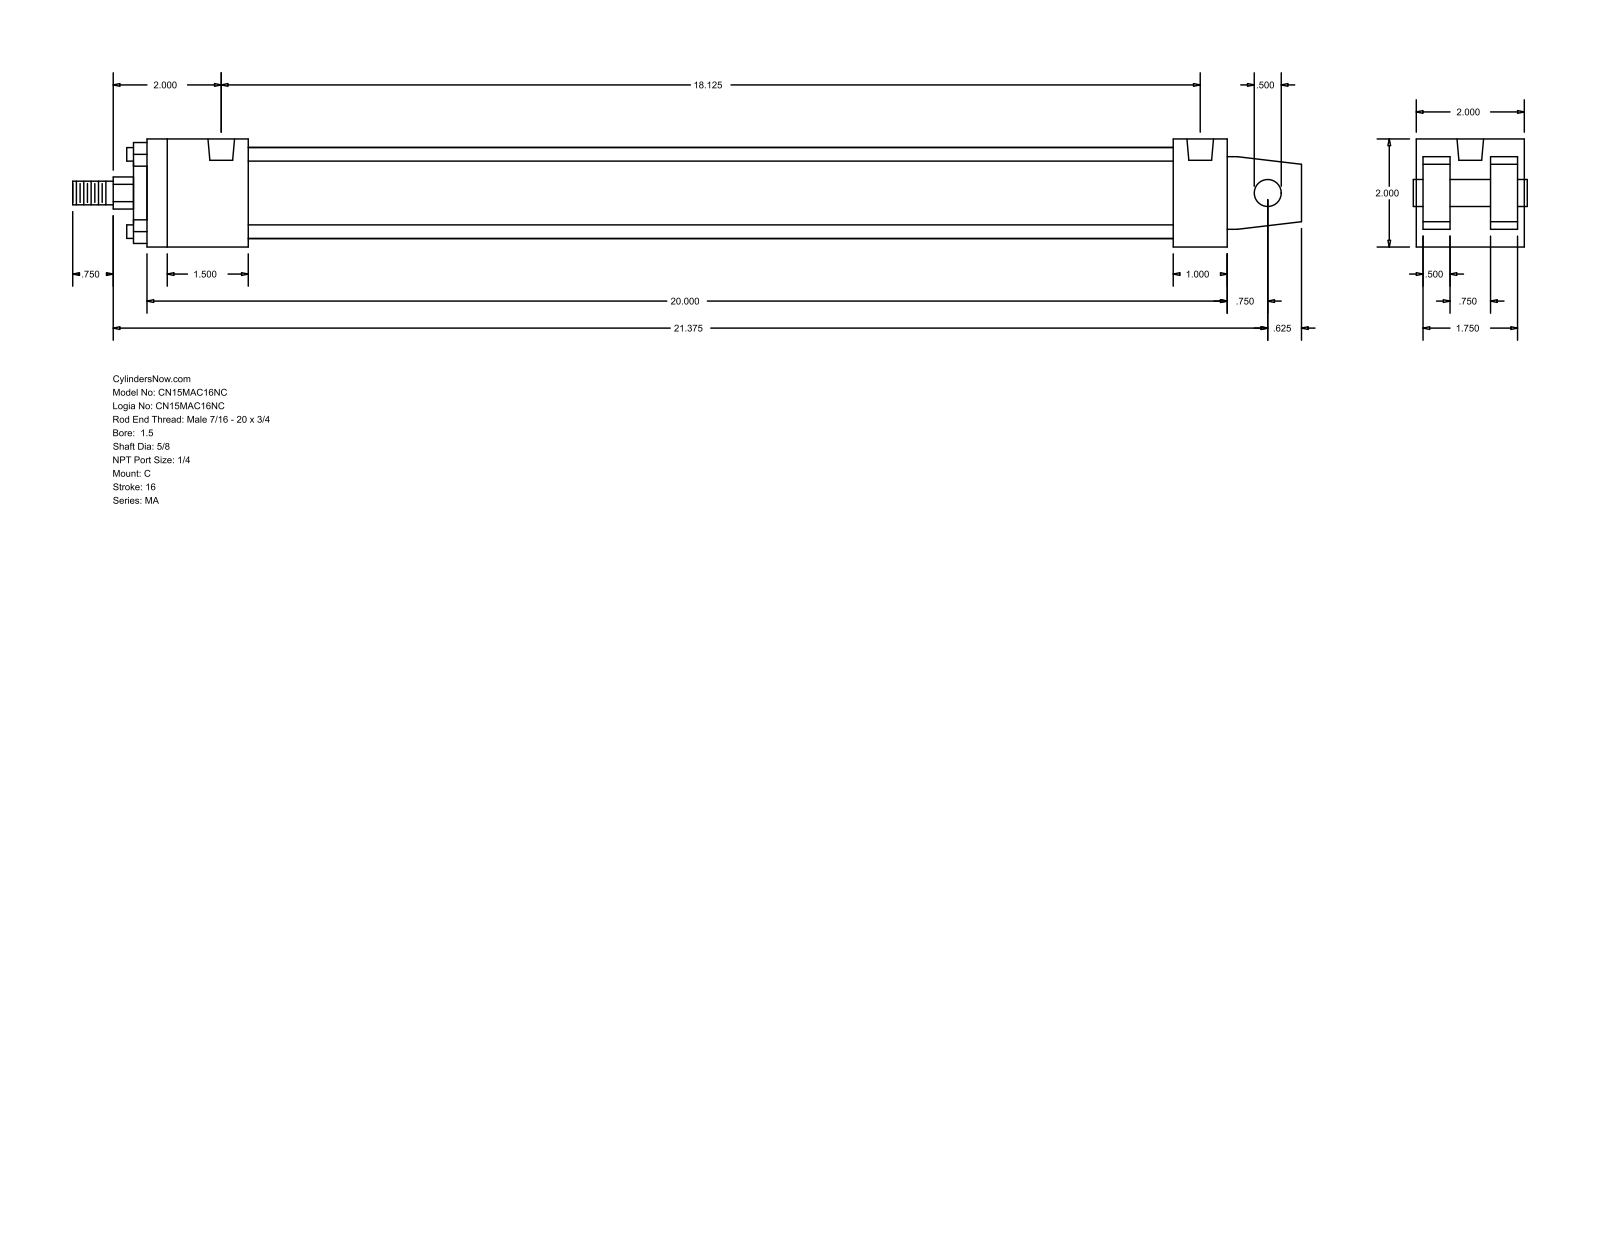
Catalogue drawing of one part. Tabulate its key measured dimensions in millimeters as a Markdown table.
| quantity | value |
| --- | --- |
| part name | MA_C__0150_0.625 |
| STEP written by | GSSL Pune (CONFIG_CONTROL_DESIGN) |
| units | millimeters |
| bodies | 0 solids, 103 faces (76 planar, 27 cylindrical, 0 other) |
| overall size | 577.85 × 50.8 × 50.8 |
| round holes (diameter × count) | 7.94 × 4, 12.49 × 2 |
| round bosses / shafts (diameter × count) | 6.35 × 4, 42.93 × 1, 28.57 × 1, 15.88 × 1, 12.7 × 1, 11.11 × 1 |
| partial cylindrical surfaces (radius × count) | 7.54 × 1 |
| main face-to-face distances | 50.8, 12.7, 34.93, 15.87, 3.17, 47.63, 31.76, 508, 25.4, 482.6 |
| hole center spacings | 460.38 |
